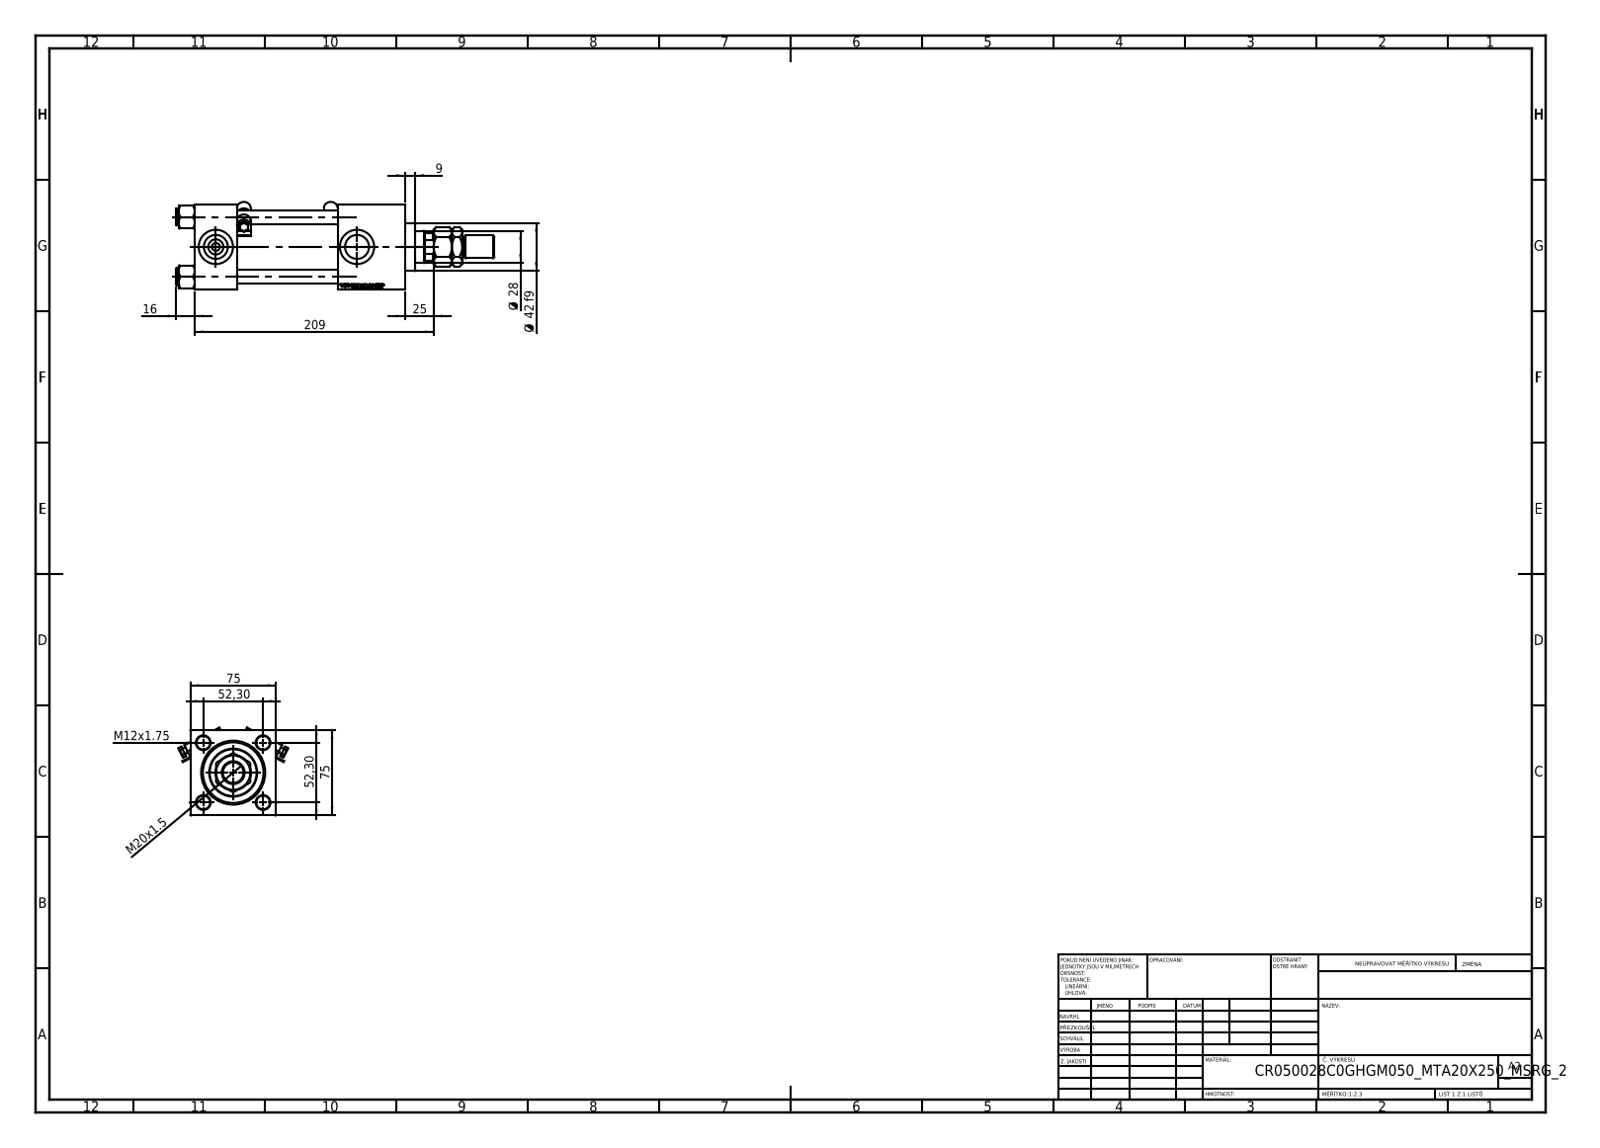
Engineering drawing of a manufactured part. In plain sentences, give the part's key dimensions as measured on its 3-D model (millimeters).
The part is named "MTA; MSRF_MSRG1; NUT_M5_C; V215CR_VCP_C (+3 more)". Its 3-D file was written by "SolidWorks 2019 (CONFIG_CONTROL_DESIGN)". It is 14 solids with 1261 faces: 577 planar, 118 cylindrical and 566 other. Overall it measures 278 by 95.81 by 76.88 millimeters. Its volume is 751 403 cubic millimeters and its surface area 178 437 square millimeters. Round holes: 4 of diameter 12, 2 of diameter 7, 2 of diameter 20.96, 2 of diameter 30, 1 of diameter 18.5, 1 of diameter 28, 1 of diameter 31, 1 of diameter 41, 1 of diameter 50, 1 of diameter 53. Round bosses or shafts: 4 of diameter 15, 2 of diameter 5, 2 of diameter 2.5, 1 of diameter 56, 1 of diameter 42, 1 of diameter 20, 1 of diameter 18. Partial cylindrical surfaces (rounded edges, fillets, slot ends): 12 of radius 0.5, 4 of radius 6, 1 of radius 13.5. The main face-to-face distances are 75, 37, 88, 125, 184, 147, 59, 155.3, 118.3, 30.3. The hole center spacings are 36.98, 52.3, 73.96, 123.5.
